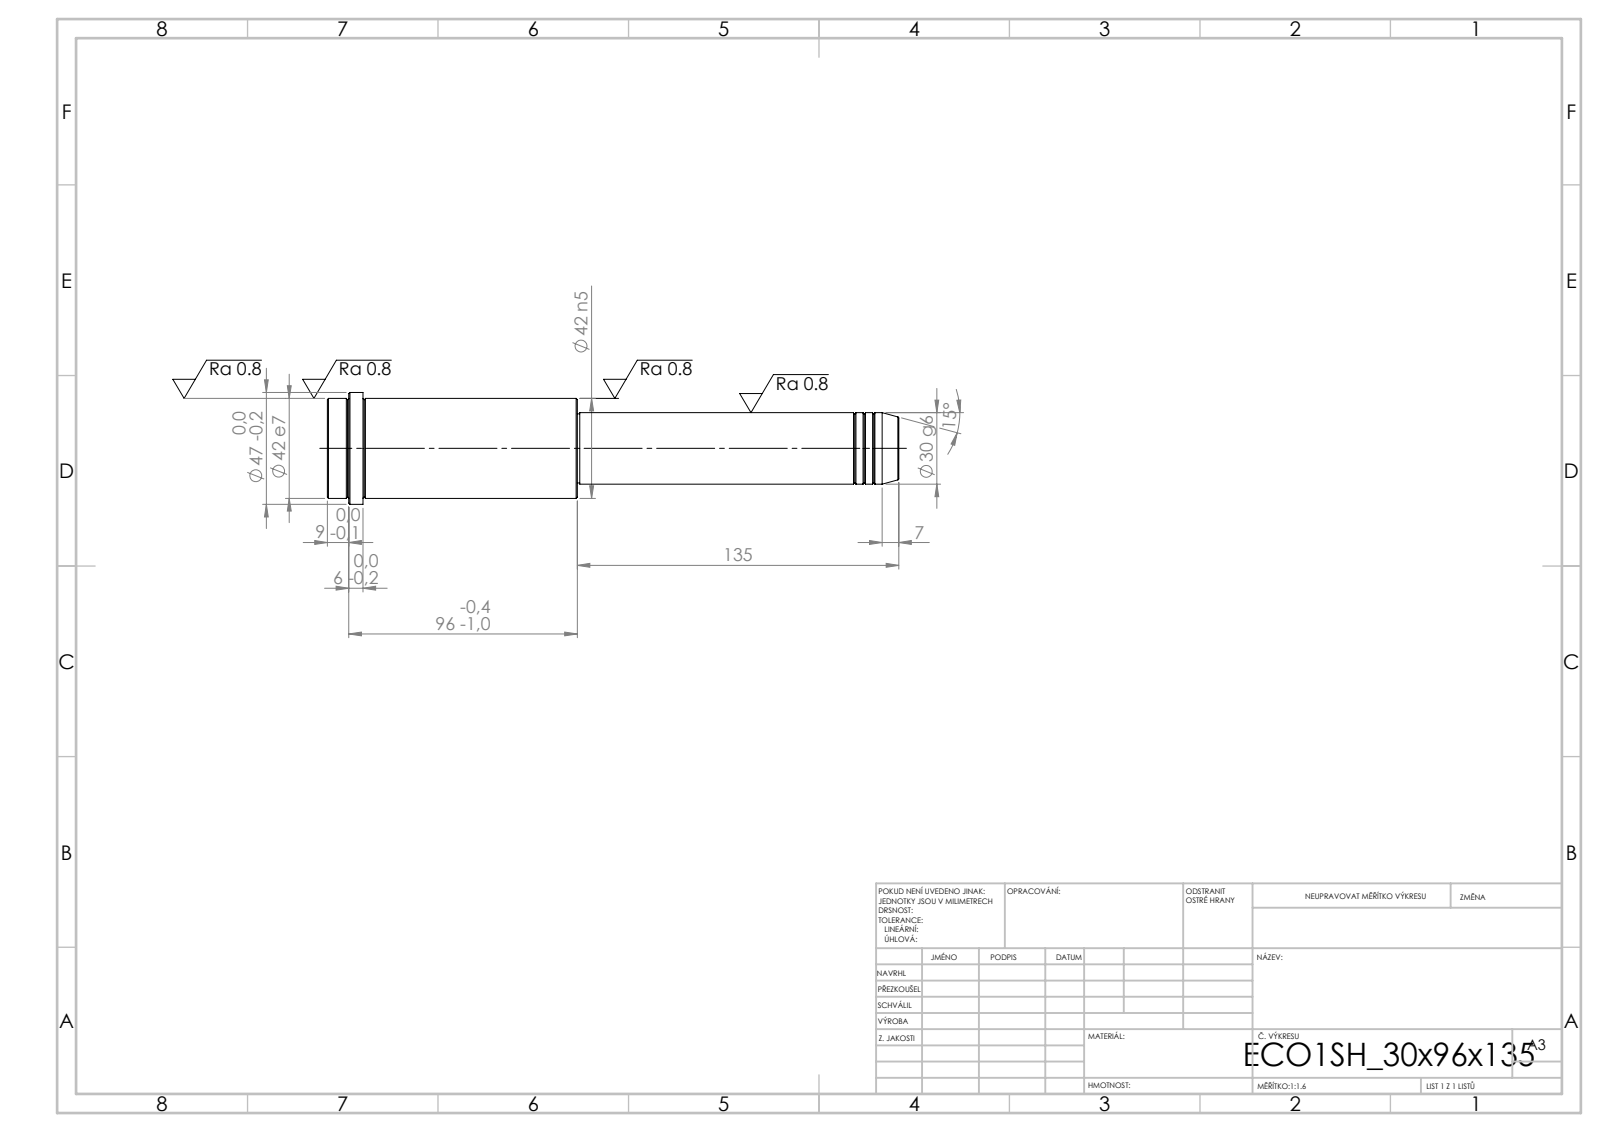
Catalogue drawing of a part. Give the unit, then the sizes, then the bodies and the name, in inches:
Units: inches
Overall size (bounding box): 9.449 × 1.85 × 1.85
Round bosses / shafts (diameter × count): ⌀1.85 ×1, ⌀1.654 ×1, ⌀1.181 ×1, ⌀1.142 ×1
Main face-to-face distances: 4.134, 5.315, 9.449, 8.858, 3.543, 0.591, 9.094, 3.78, 0.236, 0.354
Volume: 14.77 in³ · Surface area: 46.83 in²
Bodies: 1 solid, 52 faces (6 planar, 16 cylindrical, 30 other)
STEP written by: SolidWorks 2019 (CONFIG_CONTROL_DESIGN)
